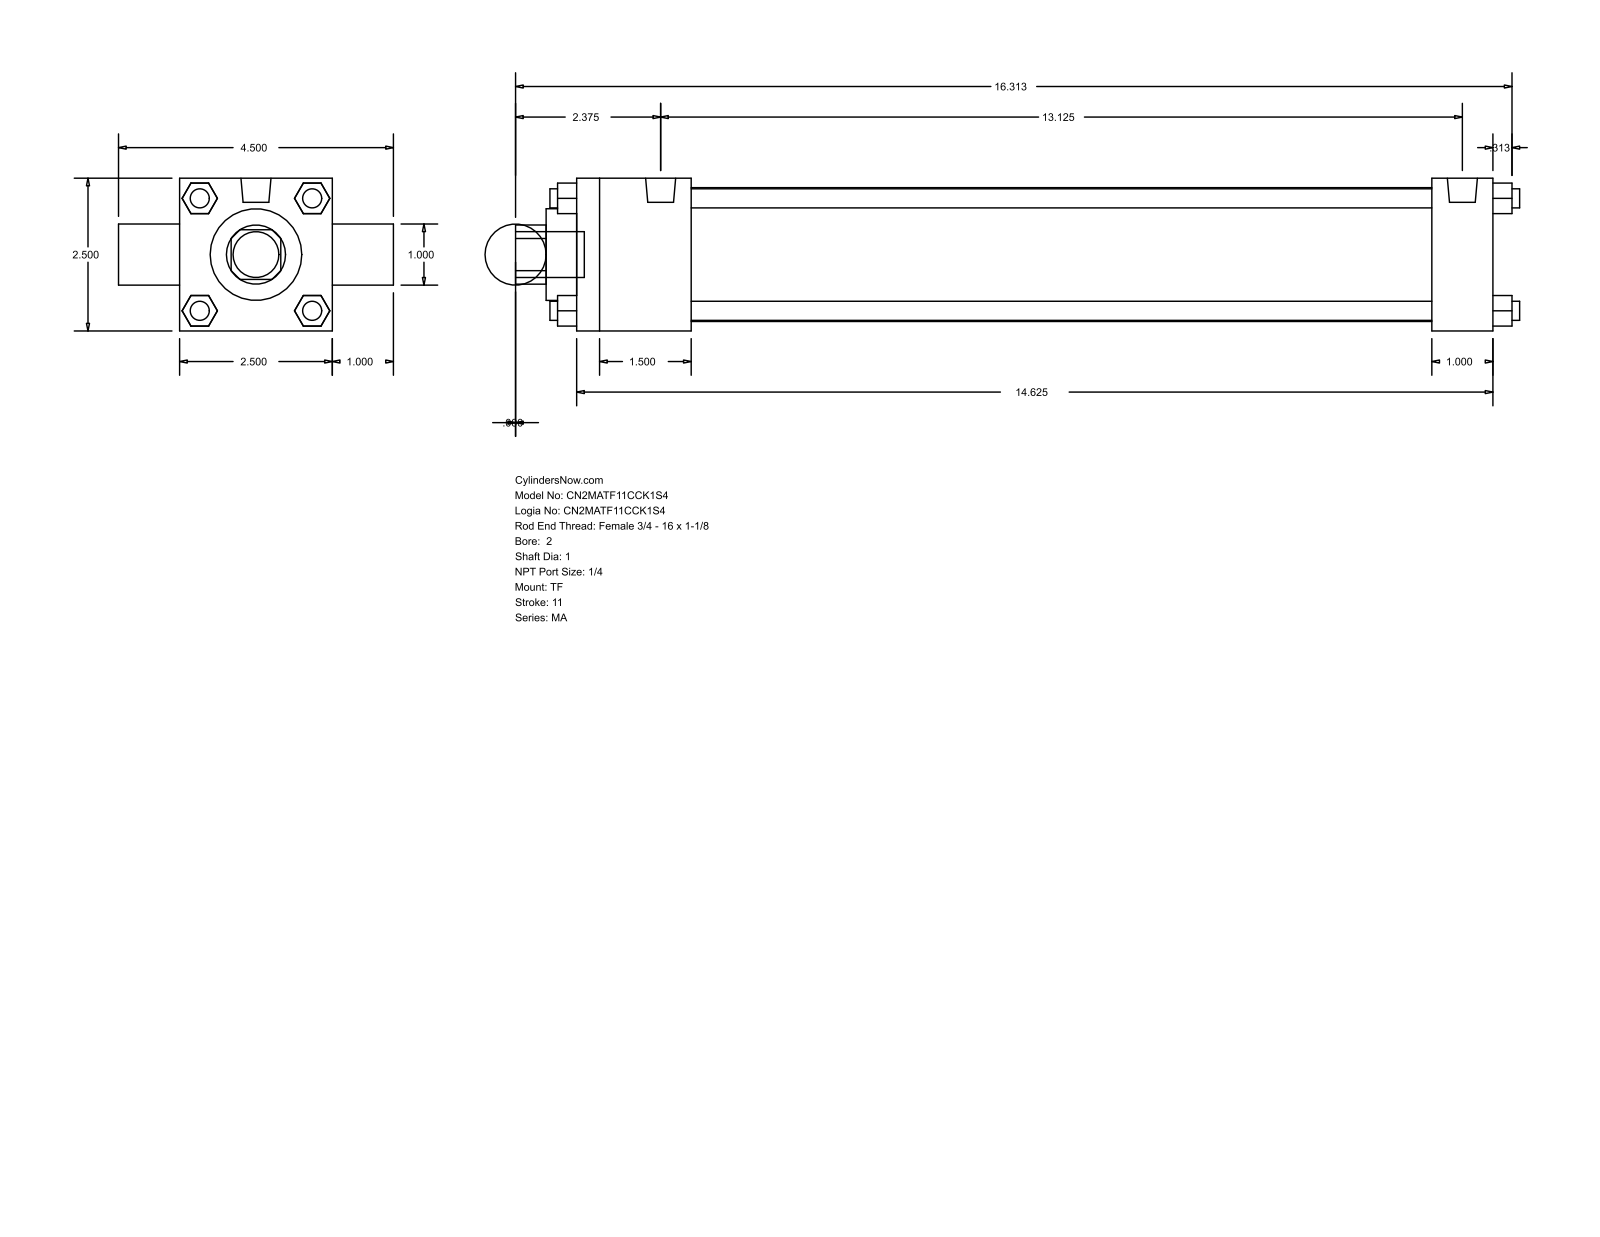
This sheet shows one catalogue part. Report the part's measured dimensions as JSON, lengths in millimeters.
{"part_name": "MA_TF__0200_1", "step_written_by": "GSSL Pune (CONFIG_CONTROL_DESIGN)", "units": "millimeters", "bodies": {"solids": 0, "faces": 120, "planar": 92, "cylindrical": 28, "other": 0}, "overall_size": [417.51, 114.3, 63.5], "round_holes": [[25.4, 2], [38.1, 1], [55.63, 1]], "round_bosses_or_shafts": [[7.94, 7], [12.49, 2], [19.05, 1]], "partial_cylinders_radius": [[12.29, 1]], "face_to_face_distances": [63.5, 25.4, 381, 12.7, 47.63, 355.6, 307.97, 333.37, 88.9, 40.47]}
